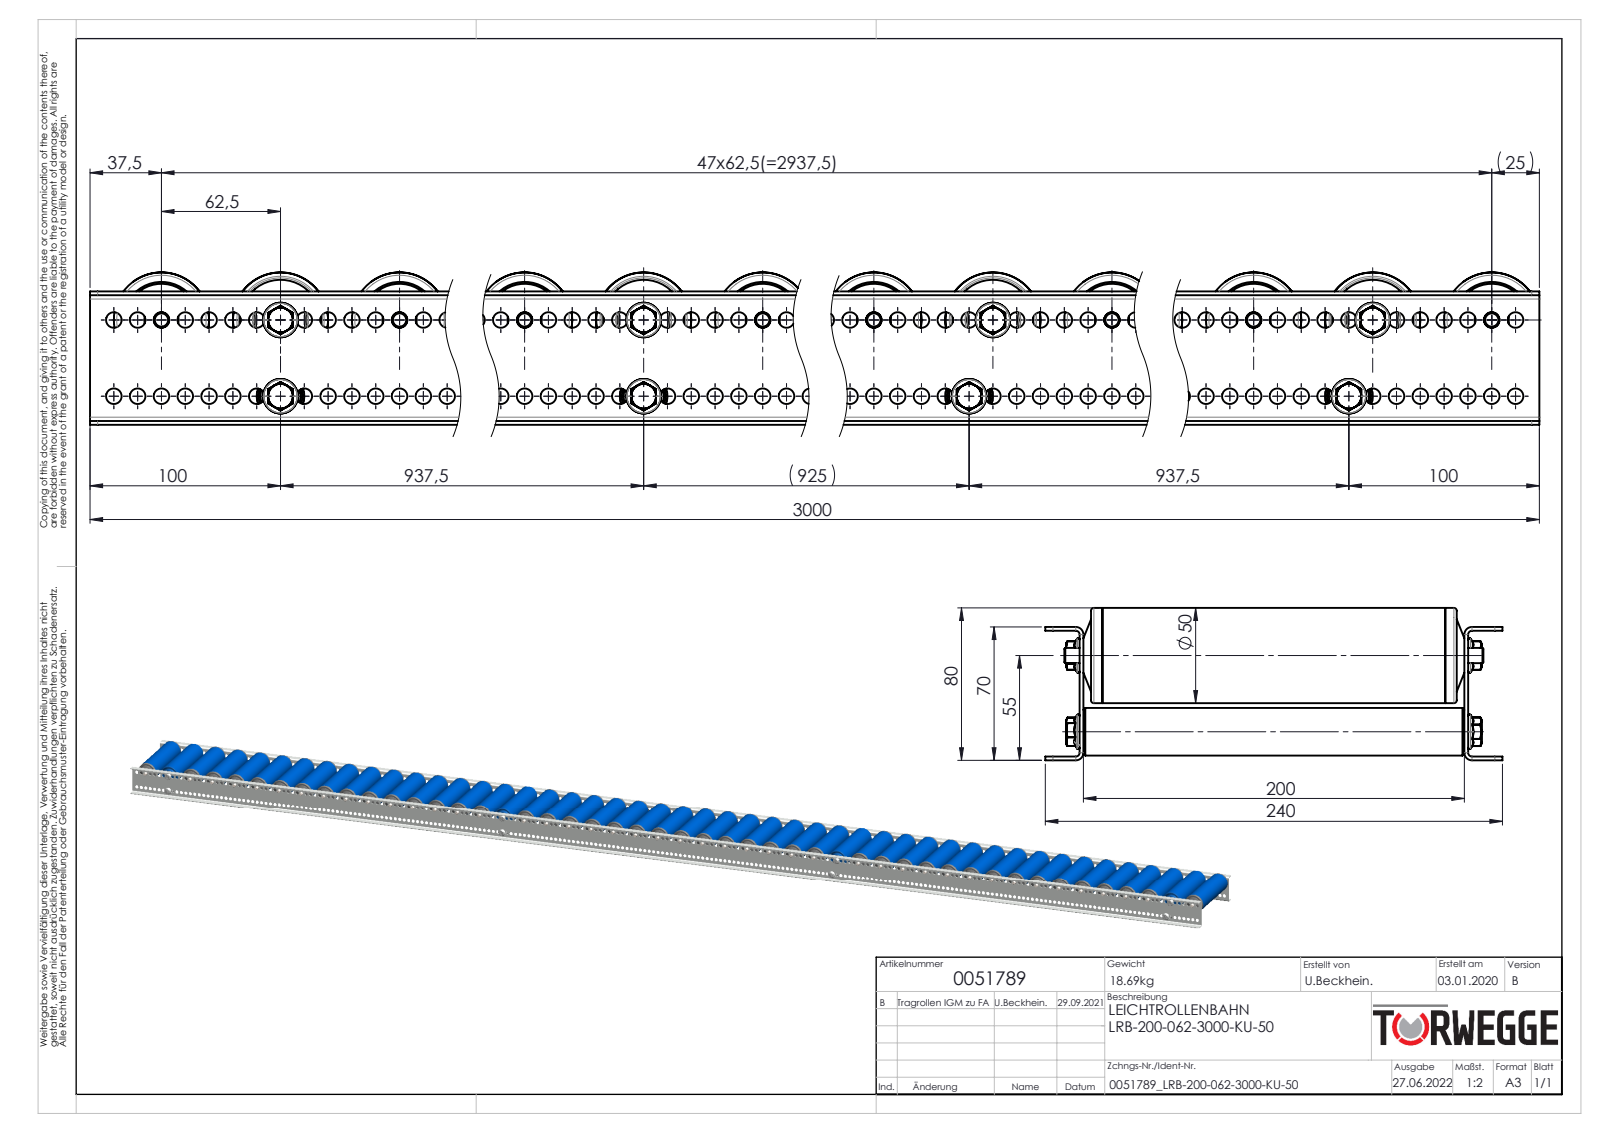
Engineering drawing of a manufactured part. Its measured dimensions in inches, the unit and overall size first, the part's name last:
Units: inches
Overall size (bounding box): 118.11 × 9.449 × 3.15
Round holes (diameter × count): ⌀0.323 ×478, ⌀0.299 ×44, ⌀0.315 ×44, ⌀0.984 ×44, ⌀1.181 ×44, ⌀1.378 ×44, ⌀1.551 ×44, ⌀1.575 ×44, ⌀0.268 ×8, ⌀0.472 ×4, ⌀0.476 ×4, ⌀0.63 ×4
Round bosses / shafts (diameter × count): ⌀1.969 ×48, ⌀1.748 ×44, ⌀1.496 ×44, ⌀1.417 ×44, ⌀1.299 ×44, ⌀0.866 ×44, ⌀0.827 ×44, ⌀0.984 ×8
Partial cylindrical surfaces — rounded edges, fillets, slot ends (radius × count): R0.024 ×88, R0.03 ×88, R0.096 ×88, R0.192 ×44, R0.276 ×44, R0.157 ×8, R0.079 ×4
Main face-to-face distances: 0.079, 7.953, 2.677, 7.874, 8.031, 7.559, 2.756, 2.598, 0.472, 0.236
Hole centre spacings: 0.492, 0.984, 1.476, 1.969, 2.461, 2.953, 3.445, 3.937
Volume: 494.4 in³ · Surface area: 9 655 in²
Bodies: 722 solids, 13620 faces (3404 planar, 6400 cylindrical, 3816 other)
Part name (STEP PRODUCT): Profil_LRB-20x70x20x2_KFG_S109080_U-PROFIL-20-70-20-2-LRB-L=3000; Druckfeder_1,2x10x30; KUT100-50x2,8-KB-A8-FA_KFG_0034512_KUT100-50x2,8-KB-A8-FA-EL=200; 0026266_Typ-KUT100-50x2,8-12 (+8 more)
STEP written by: SolidWorks 2020 (AUTOMOTIVE_DESIGN)
